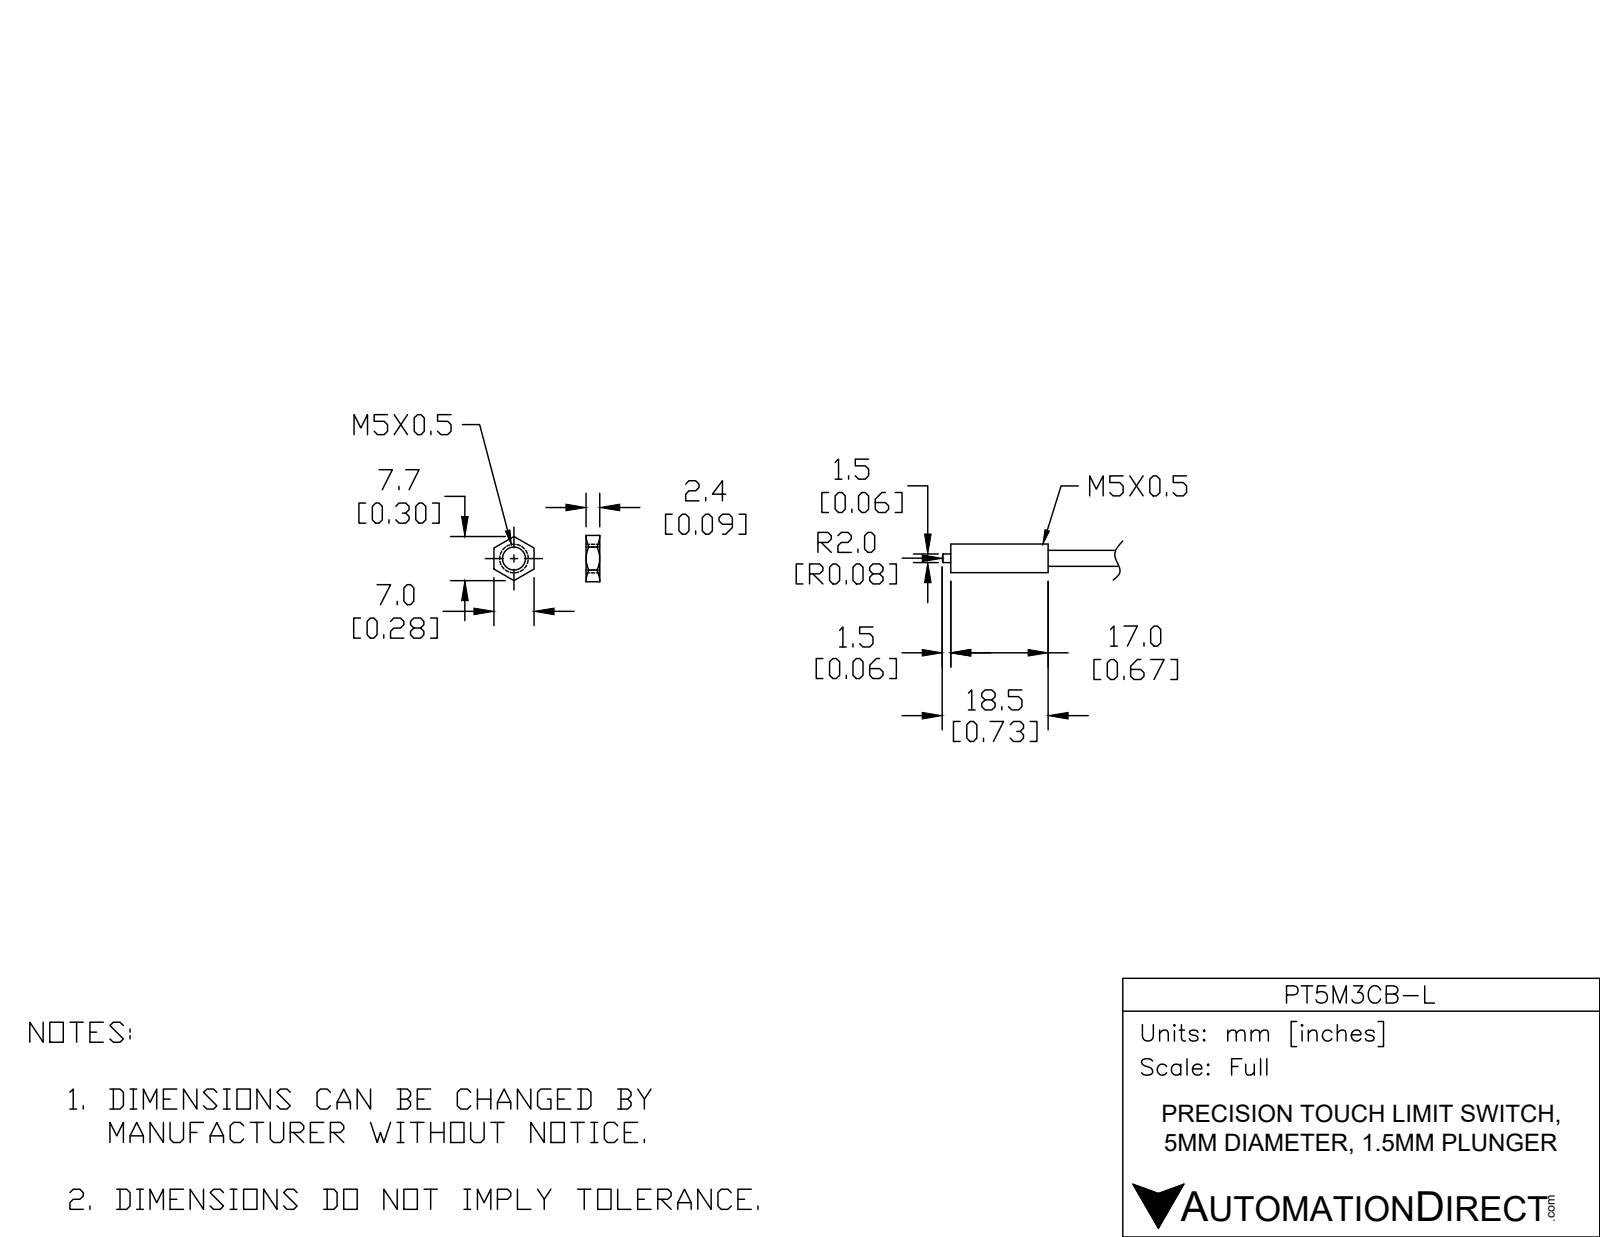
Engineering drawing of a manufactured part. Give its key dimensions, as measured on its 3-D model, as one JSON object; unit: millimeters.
{"step_written_by": "Spatial InterOp 3D (CONFIG_CONTROL_DESIGN)", "units": "millimeters", "bodies": {"solids": 2, "faces": 91, "planar": 7, "cylindrical": 79, "other": 5}, "overall_size": [173.5, 5, 5], "volume_mm3": 1481, "surface_area_mm2": 1986, "round_bosses_or_shafts": [[5, 1], [4.5, 1], [2.8, 1], [1.5, 1]], "face_to_face_distances": [17, 137, 162, 120, 145, 25, 76.5, 78.5, 172, 59.5]}
